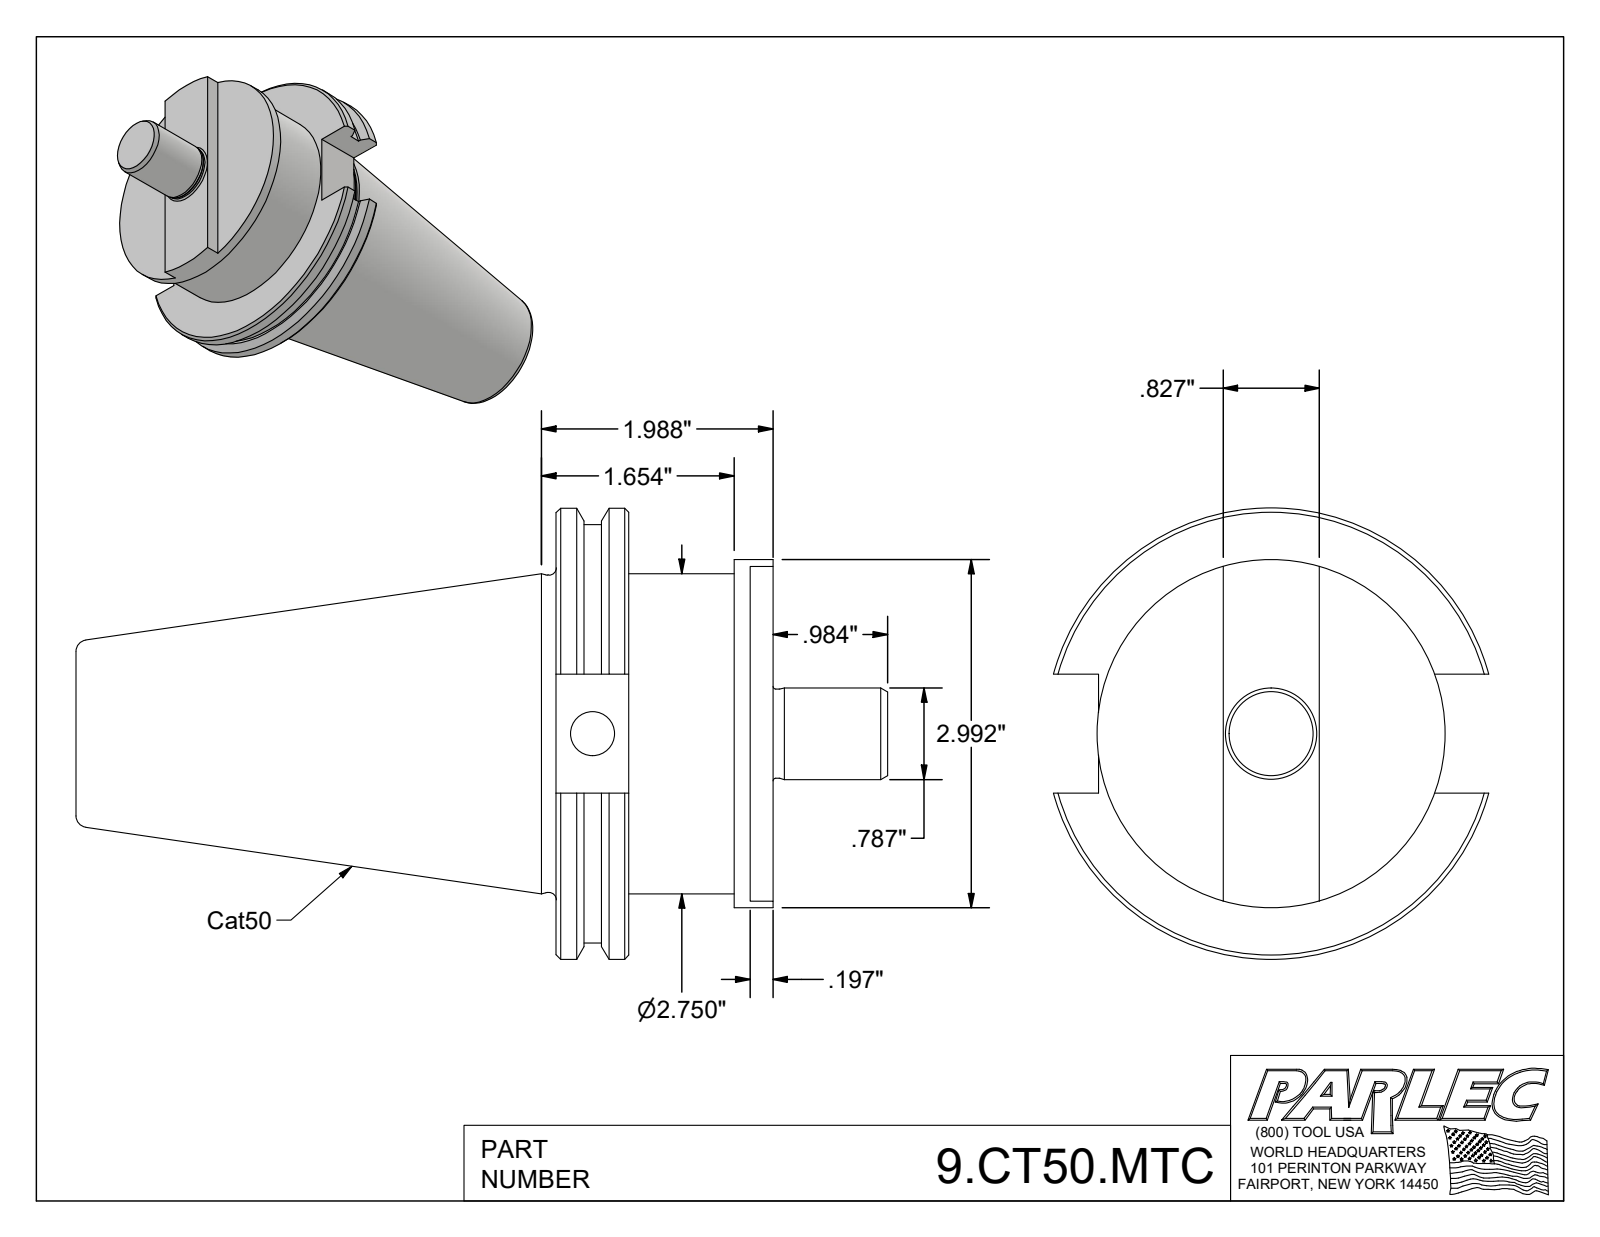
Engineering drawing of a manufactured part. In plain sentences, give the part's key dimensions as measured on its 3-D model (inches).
The part is named "9_SK_45_2 (Cat50, MTC)". Its 3-D file was written by "Autodesk Inventor 2022 (AUTOMOTIVE_DESIGN)". It is 1 solid with 58 faces: 23 planar, 15 cylindrical and 20 other. Overall it measures 6.972 by 3.875 by 3.738 inches. Its volume is 27.56 cubic inches and its surface area 80.01 square inches. Round holes: 1 of diameter 0.375, 1 of diameter 0.865, 1 of diameter 1.031, 1 of diameter 1.055. Round bosses or shafts: 1 of diameter 3.875, 1 of diameter 3.594, 1 of diameter 2.992, 1 of diameter 2.75, 1 of diameter 2.726, 1 of diameter 0.787, 1 of diameter 0.764. The main face-to-face distances are 1.041, 0.625, 1.667, 1.863, 1.238, 0.197, 1.529, 0.904, 0.138, 0.335.
